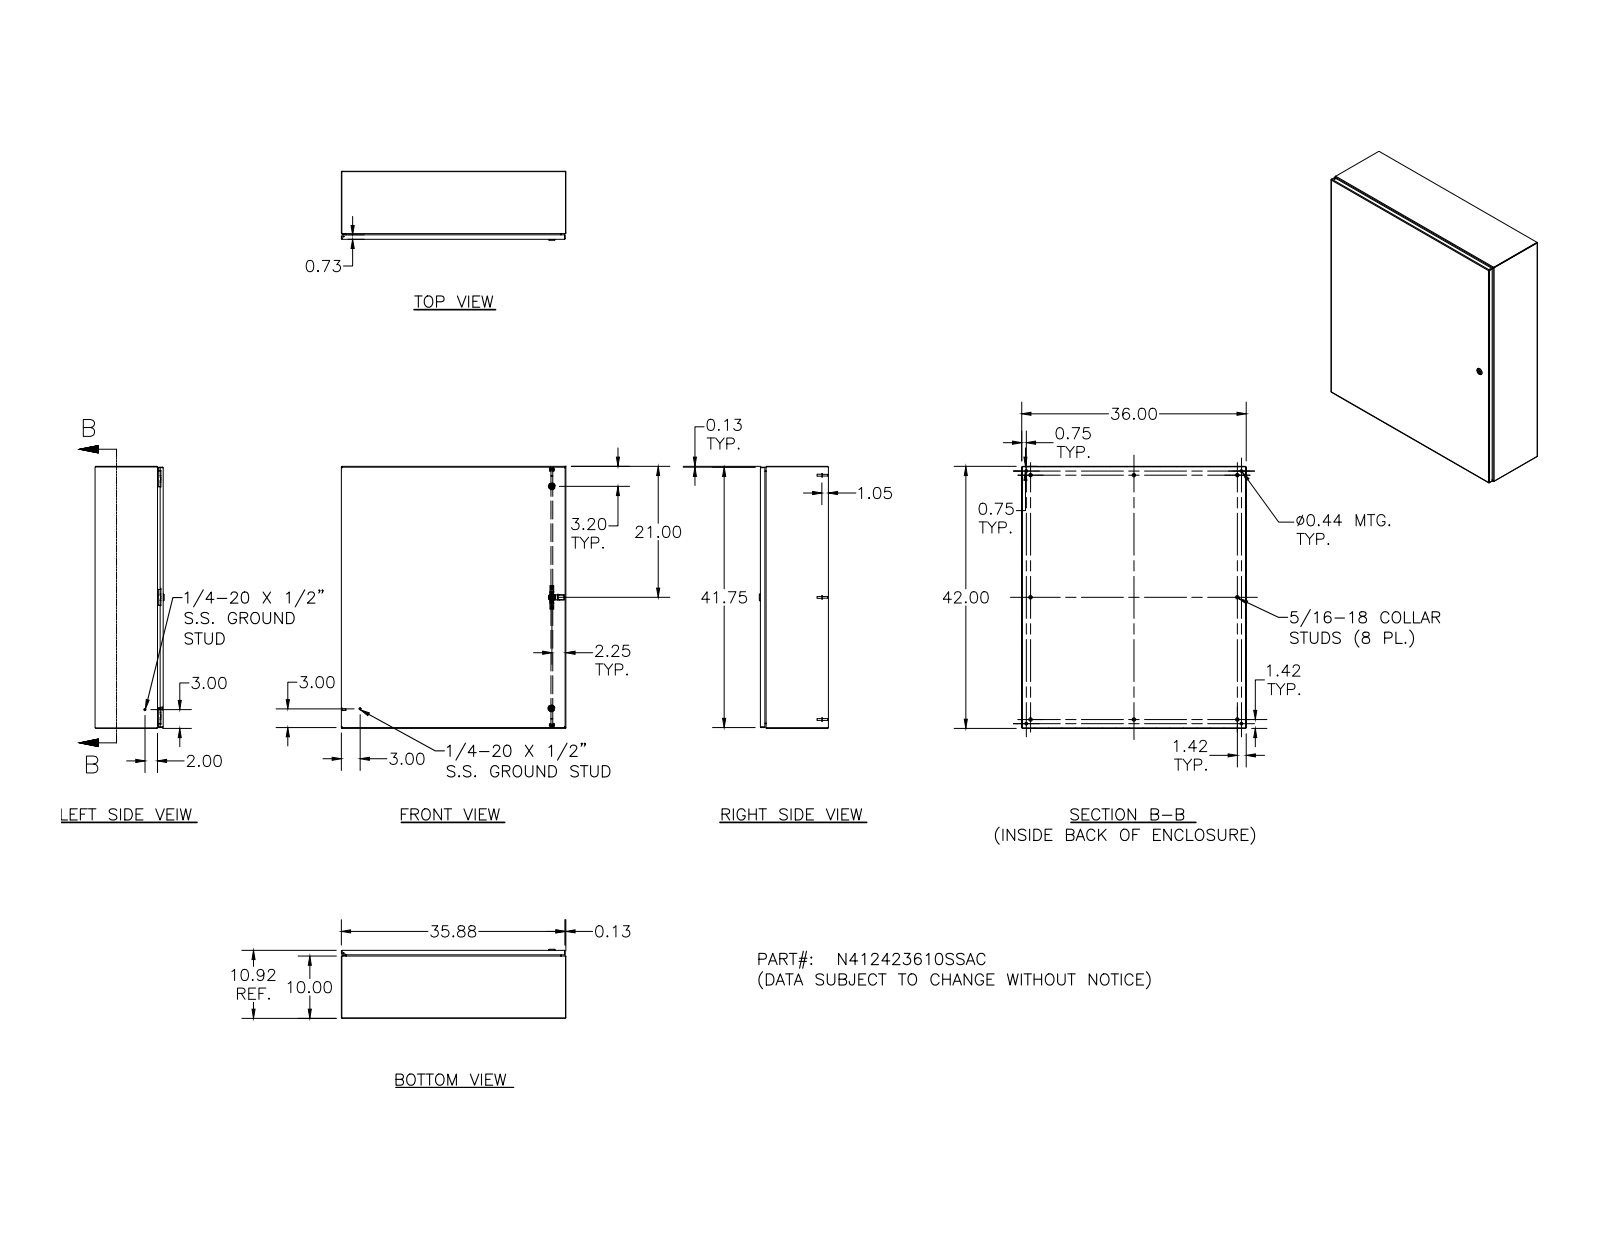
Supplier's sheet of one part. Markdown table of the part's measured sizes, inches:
| quantity | value |
| --- | --- |
| part name | N412423610SSAC; N412423610SSACBLR; N4123610SSACTB; 388151 (+8 more) |
| STEP written by | Autodesk Inventor 2011 (AUTOMOTIVE_DESIGN) |
| units | inches |
| bodies | 72 solids, 2241 faces (871 planar, 820 cylindrical, 550 other) |
| overall size | 42 × 36 × 11.075 |
| volume | 366.9 in³ |
| surface area | 9 896 in² |
| round holes (diameter × count) | 0.093 × 6, 0.152 × 6, 0.167 × 6, 0.172 × 6, 0.187 × 6, 0.197 × 5, 0.165 × 4, 0.438 × 4, 0.156 × 3, 0.106 × 2, 0.16 × 2, 0.169 × 2 |
| round bosses / shafts (diameter × count) | 0.25 × 14, 0.563 × 8, 0.3 × 8, 0.275 × 8, 0.36 × 6, 0.32 × 6, 0.256 × 6, 0.164 × 6 |
| partial cylindrical surfaces (radius × count) | 0.05 × 38, 0.031 × 32, 0.012 × 31, 0.016 × 26, 0.125 × 24, 0.02 × 20, 0.105 × 18, 0.118 × 18 |
| main face-to-face distances | 0.074, 10.843, 10.769, 10.917, 35.926, 41.926, 35.852, 36, 41.852, 42 |
| hole center spacings | 19, 38, 19.007, 0.5, 0.656, 0.66, 1.307, 1.311 |
